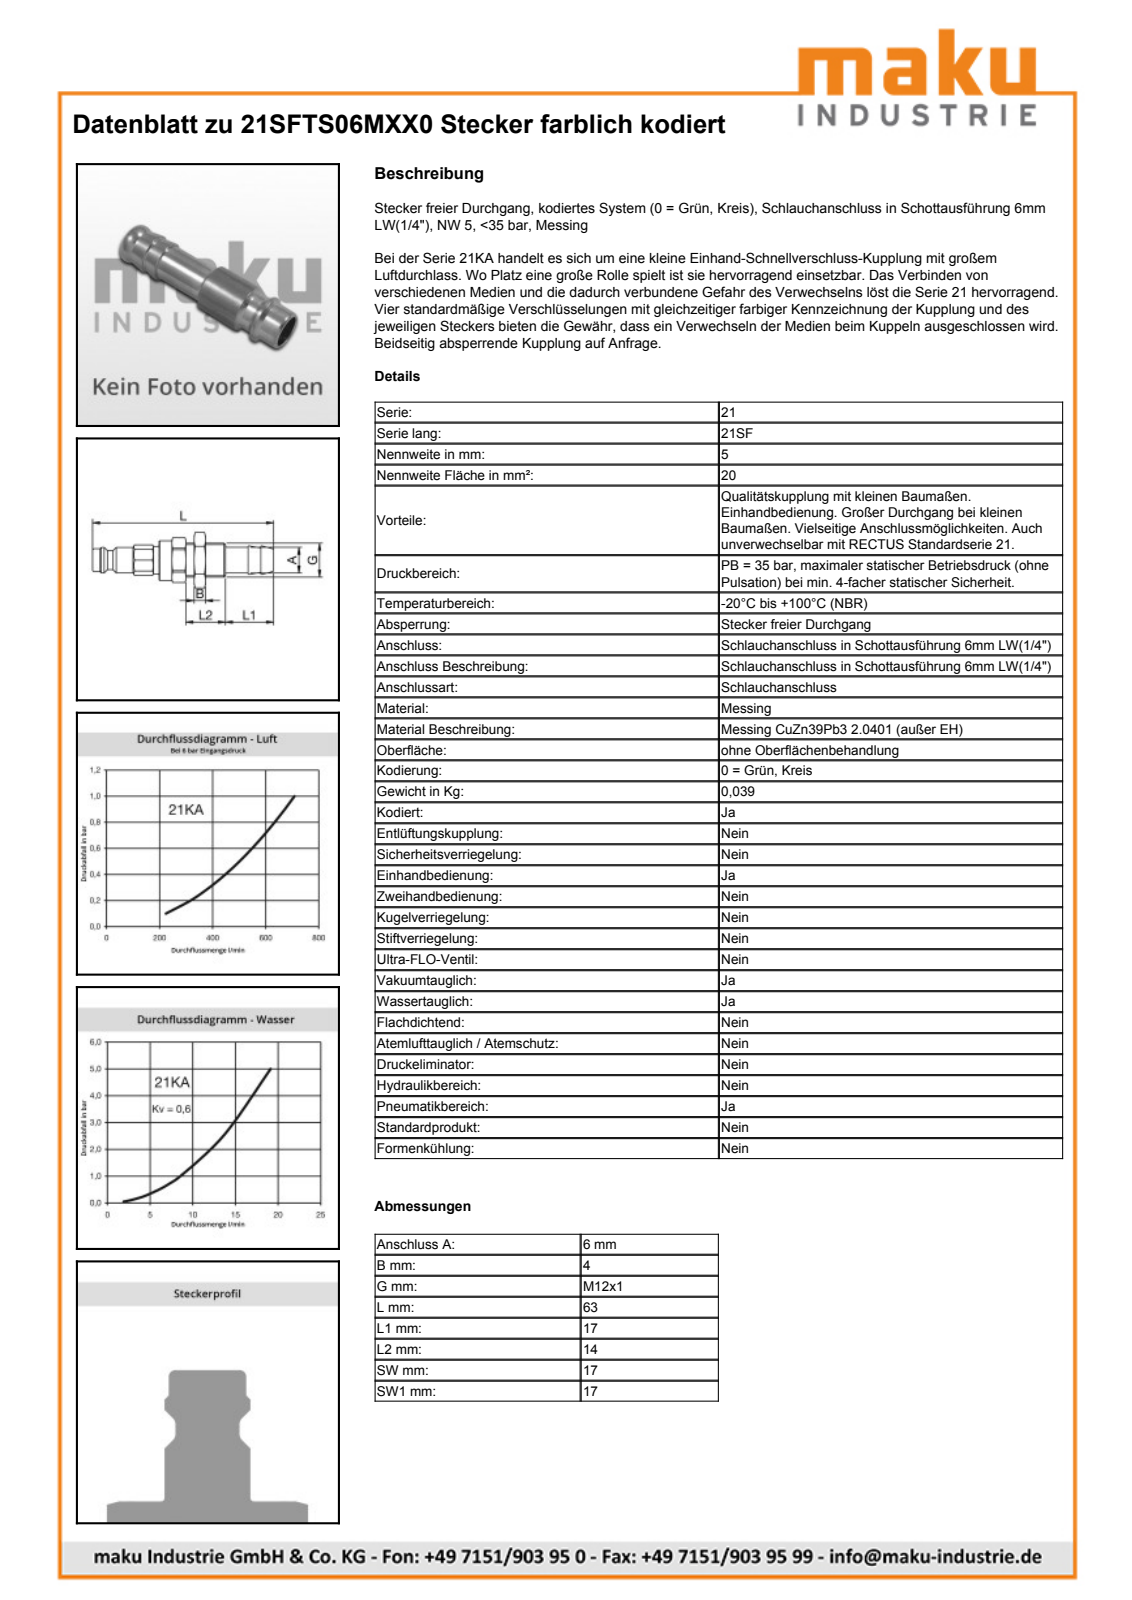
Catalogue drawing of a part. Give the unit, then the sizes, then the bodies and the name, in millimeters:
Units: millimetres
Overall size (bounding box): 63 × 19.15 × 17.41
Round holes (diameter × count): ⌀4 ×1, ⌀4.95 ×1, ⌀12 ×1, ⌀13.85 ×1, ⌀14.05 ×1
Round bosses / shafts (diameter × count): ⌀15.5 ×1, ⌀14 ×1, ⌀10.6 ×1, ⌀10.4 ×1, ⌀9 ×1, ⌀8.1 ×1, ⌀6.65 ×1, ⌀6.05 ×1
Partial cylindrical surfaces — rounded edges, fillets, slot ends (radius × count): R9.57 ×1
Main face-to-face distances: 17, 4, 8.85, 4.85, 17.35, 13.35, 8.5, 4.5, 9.15, 12.85
Volume: 4 905 mm³ · Surface area: 4 391 mm²
Bodies: 3 solids, 96 faces (24 planar, 27 cylindrical, 45 other)
Part name (STEP PRODUCT): D113123; D113124; D113125; D104664
STEP written by: Autodesk Inventor 2013 (AUTOMOTIVE_DESIGN)
